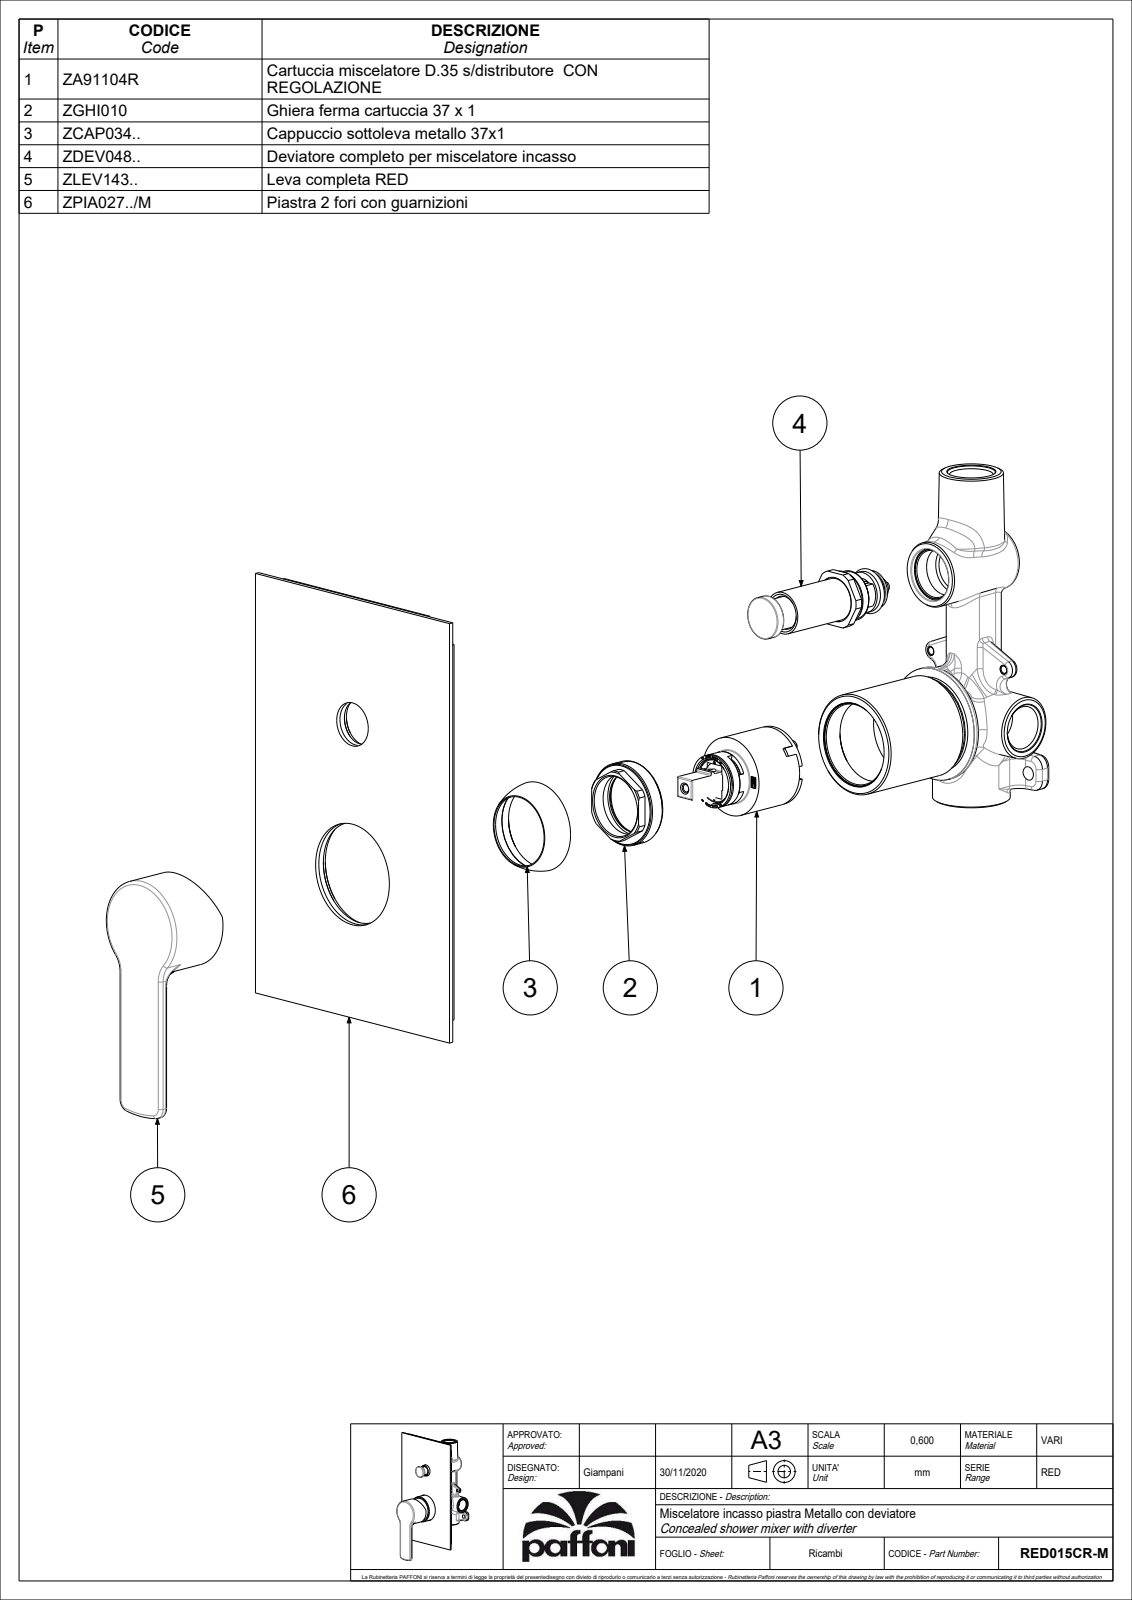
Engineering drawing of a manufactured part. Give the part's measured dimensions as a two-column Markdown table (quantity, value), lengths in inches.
| quantity | value |
| --- | --- |
| part name | RED015CR-M |
| STEP written by | CREO PARAMETRIC BY PTC INC, 2020044 (CONFIG_CONTROL_DESIGN) |
| units | inches |
| bodies | 5 solids, 1007 faces (568 planar, 244 cylindrical, 195 other) |
| overall size | 8.268 × 4.724 × 2.129 |
| volume | 5.435 in³ |
| surface area | 122.1 in² |
| round holes (diameter × count) | 0.13 × 2, 0.157 × 2, 0.768 × 2, 0.118 × 1, 0.177 × 1, 0.197 × 1, 0.413 × 1, 0.583 × 1, 0.783 × 1, 1.055 × 1, 1.142 × 1, 1.22 × 1 |
| round bosses / shafts (diameter × count) | 1.764 × 1, 1.693 × 1, 1.378 × 1, 0.925 × 1, 0.921 × 1, 0.858 × 1, 0.736 × 1, 0.732 × 1 |
| partial cylindrical surfaces (radius × count) | 0.02 × 45, 0.006 × 11, 0.012 × 4, 0.059 × 4, 0.039 × 2, 0.197 × 2, 0.394 × 2, 0.276 × 1 |
| main face-to-face distances | 0.079, 1.933, 1.854, 0.177, 2.11, 2.031, 0.374, 0.453, 0.354, 0.217 |
| hole center spacings | 0.492, 2.677 |
